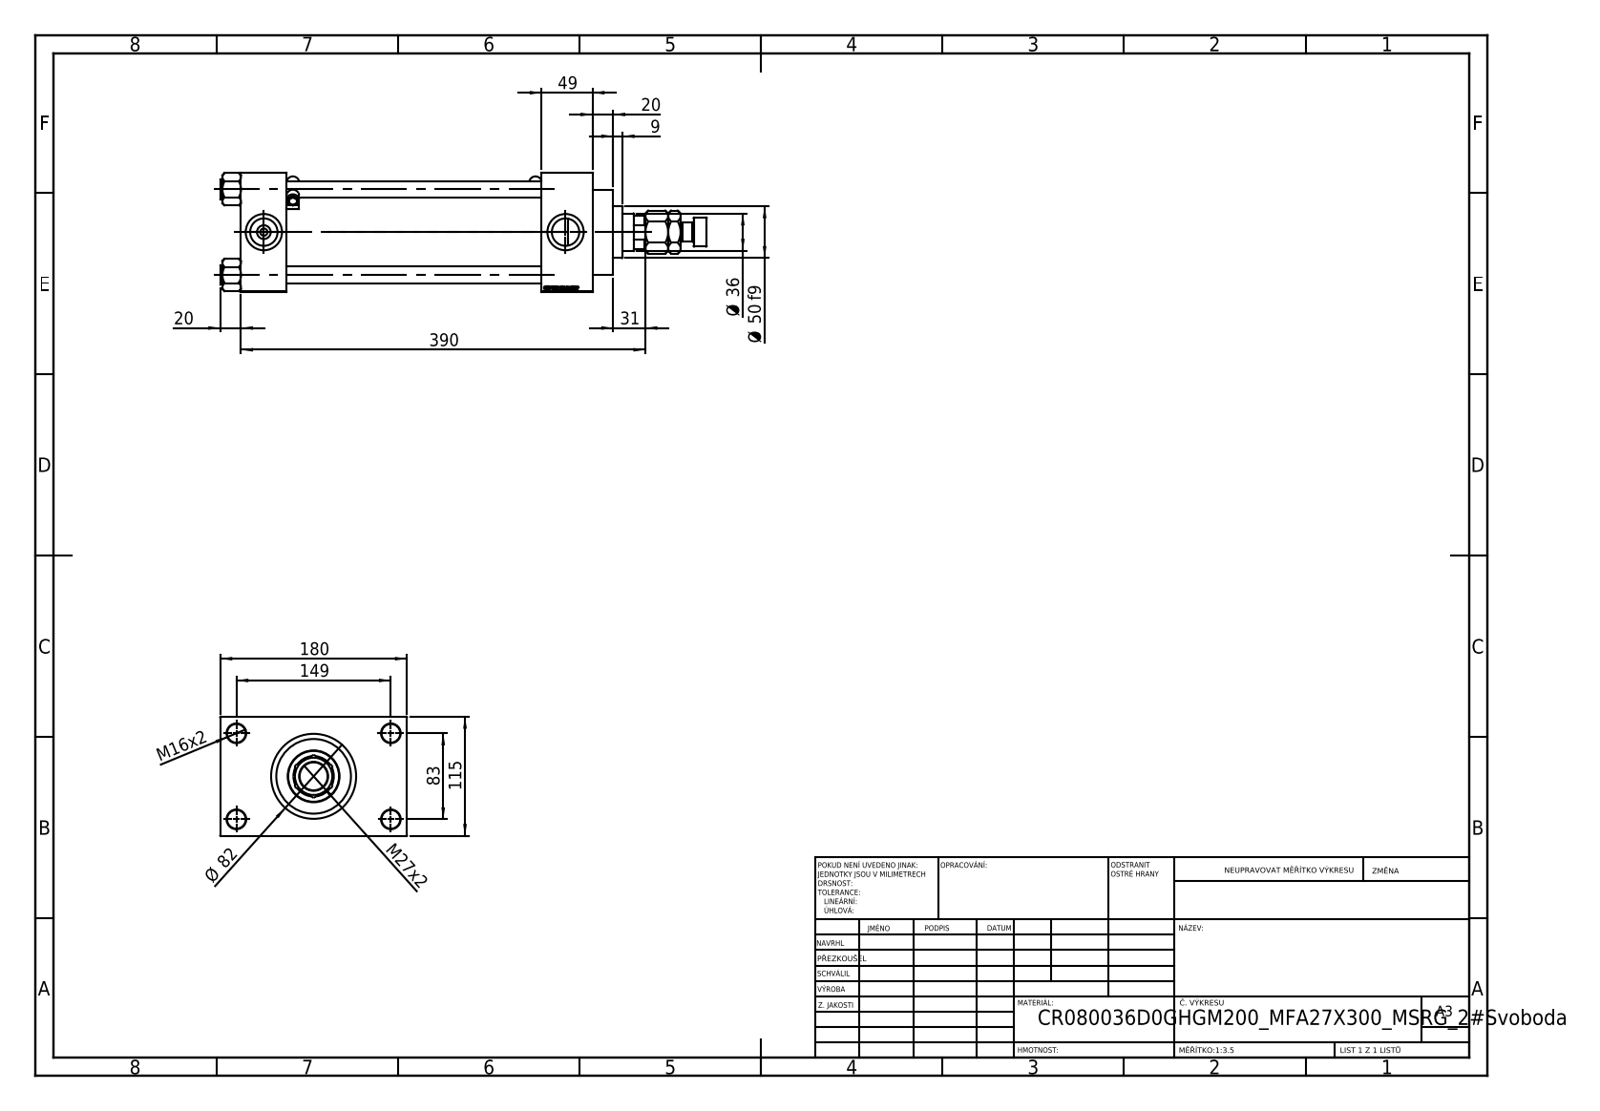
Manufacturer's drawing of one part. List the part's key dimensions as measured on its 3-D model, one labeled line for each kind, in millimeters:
Part name (STEP PRODUCT): V215CR_VCP_D; MSRF_MSRG1; V215CR_D_Body; V215_VC_A (+3 more)
STEP written by: SolidWorks 2019 (CONFIG_CONTROL_DESIGN)
Units: millimetres
Bodies: 14 solids, 1267 faces (597 planar, 120 cylindrical, 550 other)
Overall size (bounding box): 469 × 180 × 115
Volume: 2 505 000 mm³ · Surface area: 460 519 mm²
Round holes (diameter × count): ⌀16 ×4, ⌀18 ×4, ⌀7 ×2, ⌀26.44 ×2, ⌀35 ×2, ⌀25.5 ×1, ⌀36 ×1, ⌀39 ×1, ⌀61 ×1, ⌀72 ×1, ⌀80 ×1
Round bosses / shafts (diameter × count): ⌀19 ×4, ⌀5 ×2, ⌀2.5 ×2, ⌀86 ×1, ⌀82 ×1, ⌀50 ×1, ⌀28 ×1, ⌀18 ×1
Partial cylindrical surfaces — rounded edges, fillets, slot ends (radius × count): R0.5 ×12, R6 ×4, R17.5 ×1
Main face-to-face distances: 115, 246, 295, 49, 44, 290, 339, 32.5, 147.5, 90
Hole centre spacings: 33.15, 58.48, 82.7, 85.28, 89.24, 115.85, 142.43, 83
